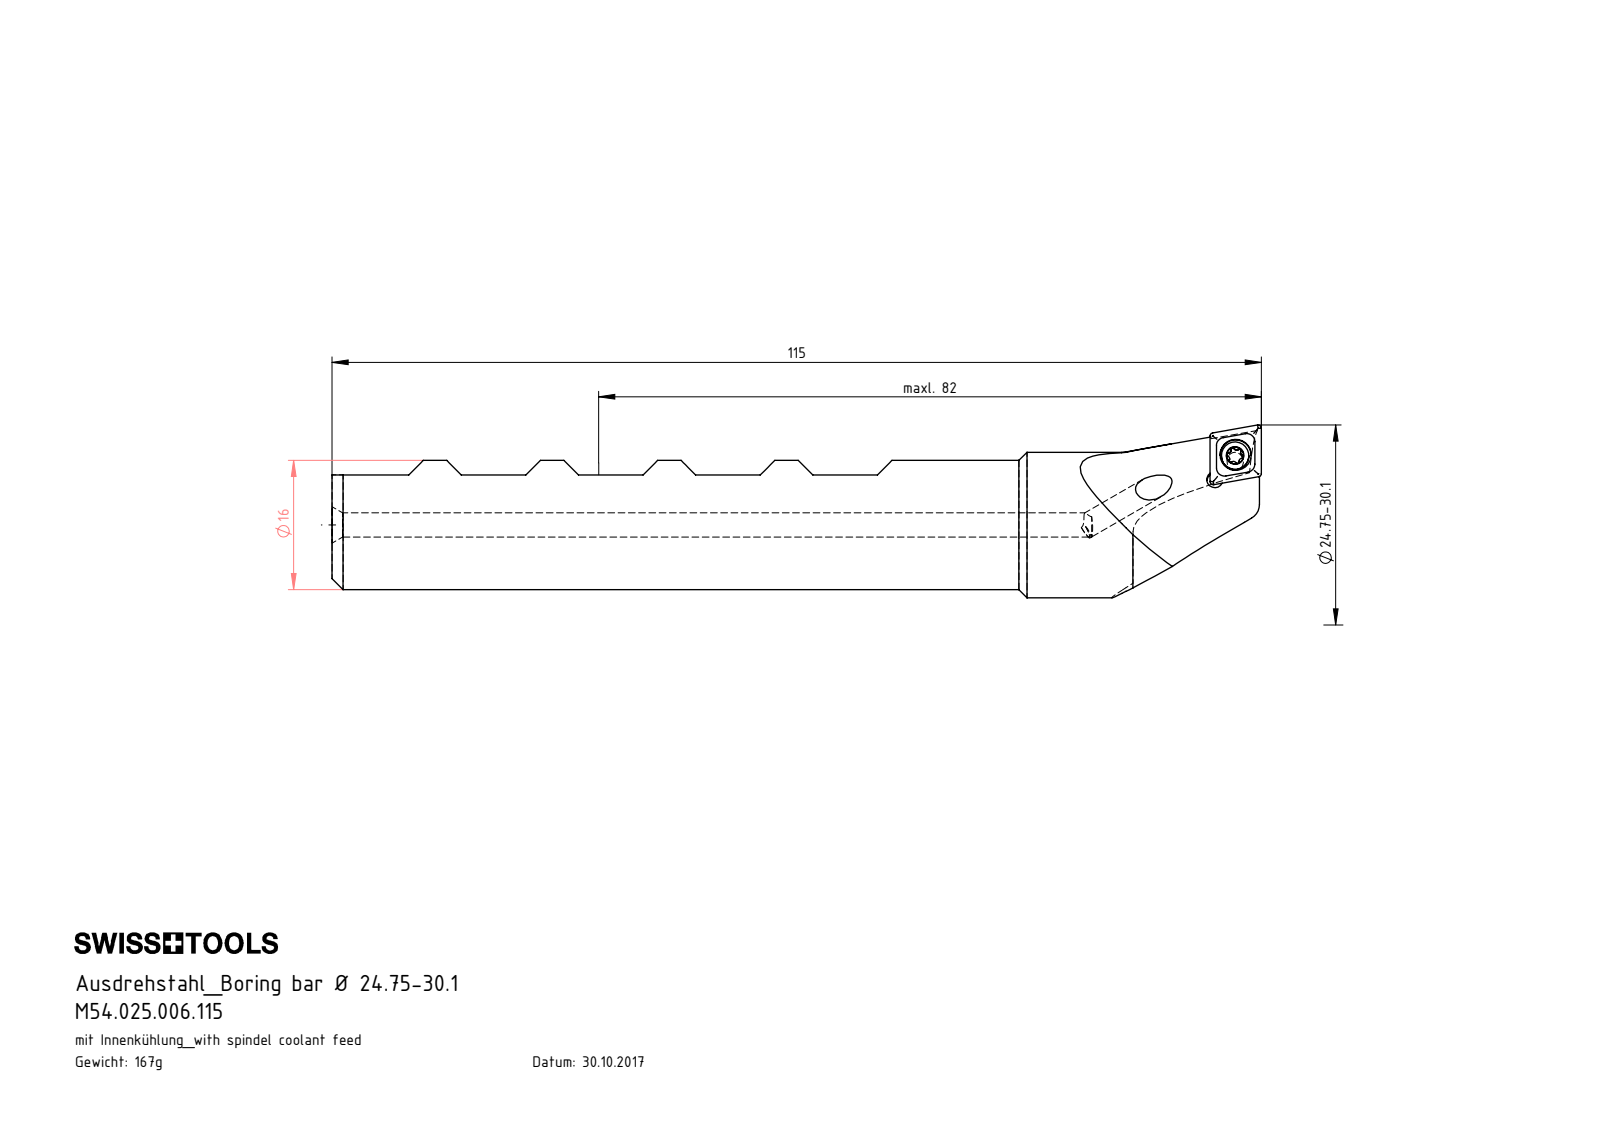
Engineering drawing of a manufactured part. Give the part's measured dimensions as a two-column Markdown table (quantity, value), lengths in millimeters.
| quantity | value |
| --- | --- |
| part name | B25.WCA.K11.115; WCA-ER2.001.006_A; CCMT060204; B25-WCA.K11.115_A |
| STEP written by | SolidWorks 2017 (AUTOMOTIVE_DESIGN) |
| units | millimeters |
| bodies | 3 solids, 110 faces (42 planar, 27 cylindrical, 41 other) |
| overall size | 115 × 21.38 × 18.92 |
| volume | 21 230 mm³ |
| surface area | 7 292 mm² |
| round holes (diameter × count) | 3 × 2, 2 × 1, 2.05 × 1, 2.8 × 1, 3.85 × 1 |
| round bosses / shafts (diameter × count) | 18 × 1, 16 × 1, 3.4 × 1, 2.5 × 1 |
| partial cylindrical surfaces (radius × count) | 0.21 × 6, 0.36 × 5, 0.36 × 1, 2 × 1, 9.2 × 1, 12 × 1 |
| main face-to-face distances | 10.25, 7.9, 20.5, 10.08, 2.18, 30.76, 20.51, 30.75, 10.26, 41.01 |
| hole center spacings | 3.89, 3.99 |
